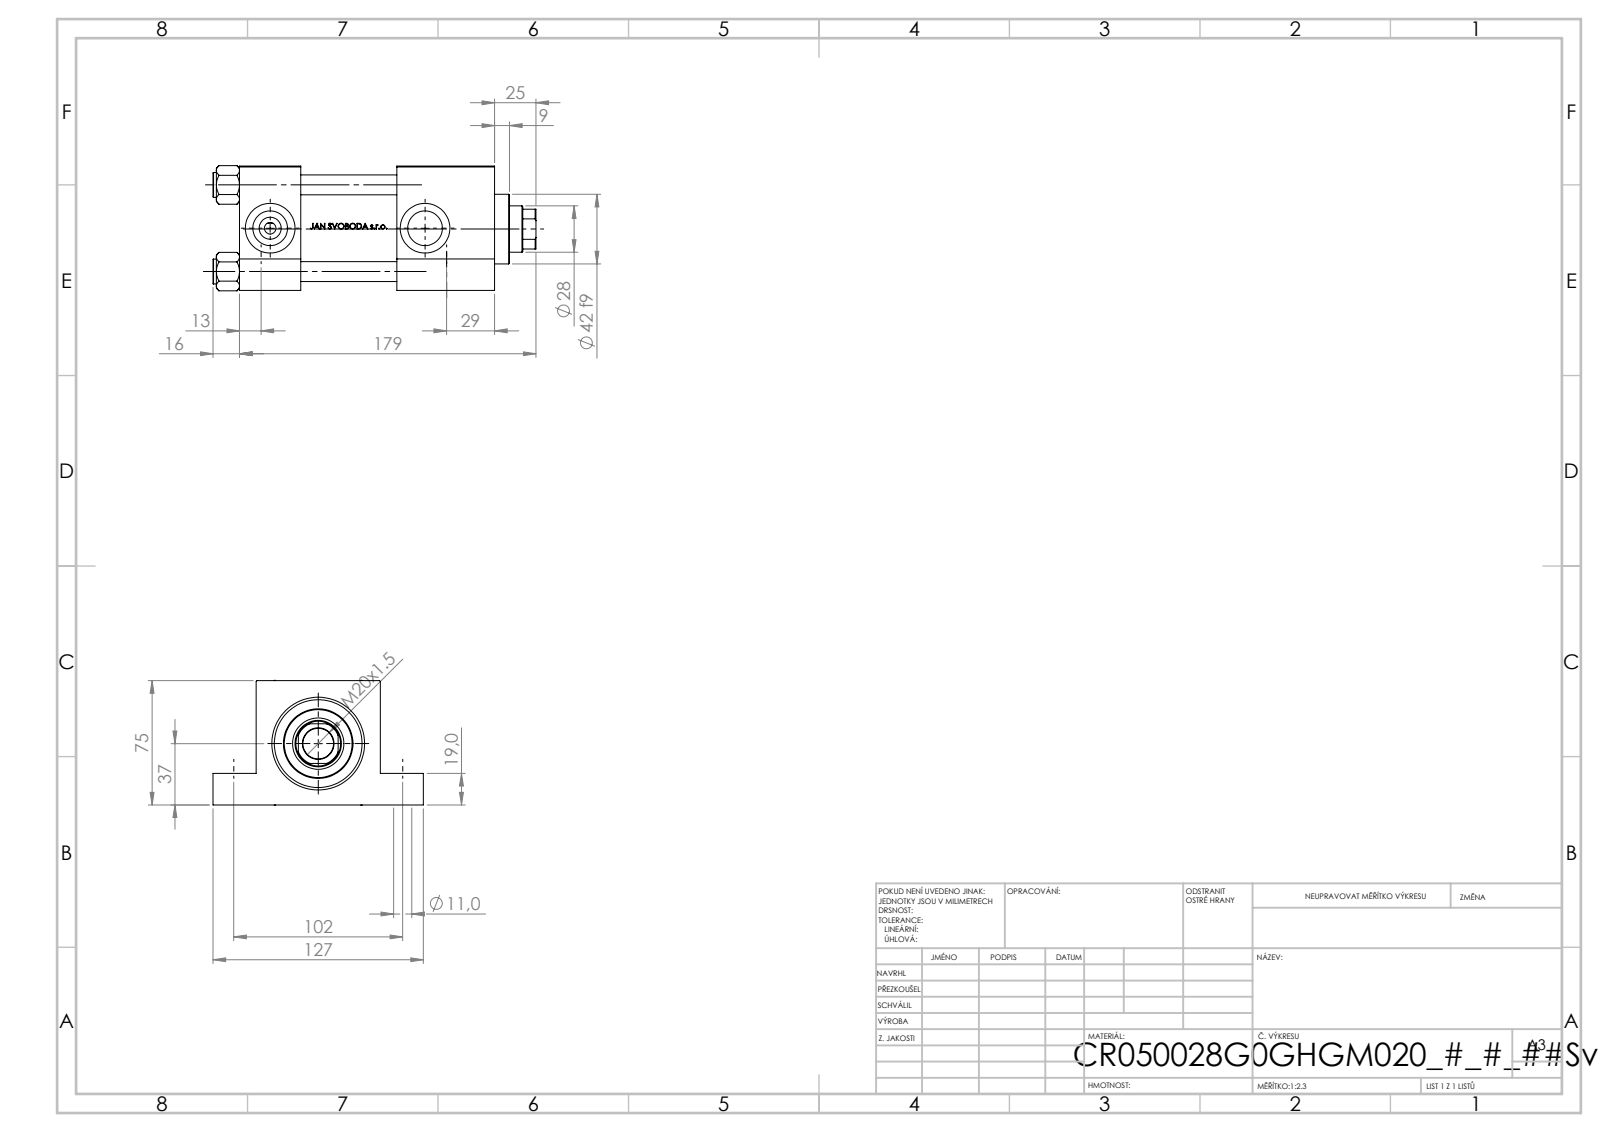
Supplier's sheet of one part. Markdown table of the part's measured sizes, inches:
| quantity | value |
| --- | --- |
| part name | V215CR_G_Body; V215_VC_A; V215CR_G_TYCINKA; NUT_M5_G (+1 more) |
| STEP written by | SolidWorks 2019 (CONFIG_CONTROL_DESIGN) |
| units | inches |
| bodies | 11 solids, 1087 faces (431 planar, 124 cylindrical, 532 other) |
| overall size | 7.677 × 5 × 2.974 |
| volume | 46.86 in³ |
| surface area | 252.6 in² |
| round holes (diameter × count) | 0.472 × 4, 0.433 × 3, 0.276 × 2, 0.825 × 2, 1.181 × 2, 0.433 × 1, 0.728 × 1, 1.102 × 1, 1.22 × 1, 1.614 × 1, 1.969 × 1, 2.087 × 1 |
| round bosses / shafts (diameter × count) | 0.591 × 4, 2.205 × 1, 1.654 × 1 |
| partial cylindrical surfaces (radius × count) | 0.531 × 1 |
| main face-to-face distances | 2.953, 1.457, 6.063, 4.606, 0.748, 2.205, 3.74, 2.283, 2.323, 1.024 |
| hole center spacings | 2.059, 1.442, 1.47, 2.912, 4.016, 4.409, 5.964, 3.681 |
